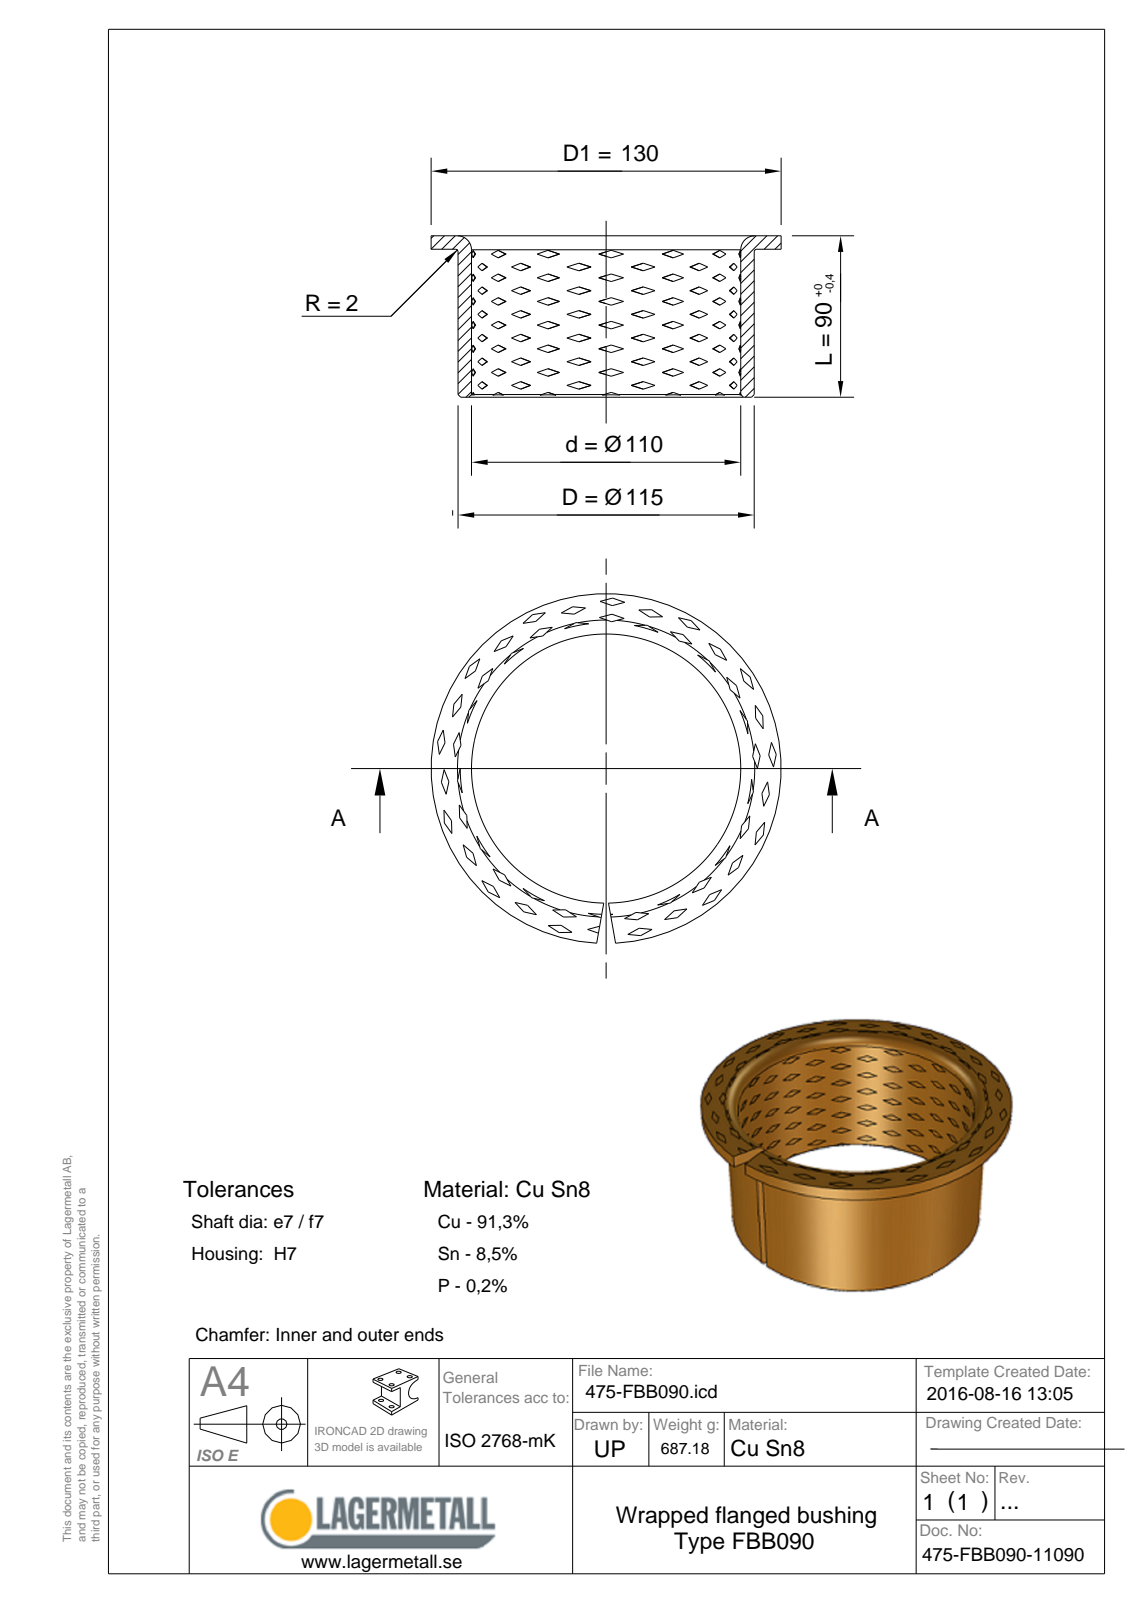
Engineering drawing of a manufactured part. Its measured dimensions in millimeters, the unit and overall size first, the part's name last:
Units: millimetres
Overall size (bounding box): 130 × 129.96 × 90
Round holes (diameter × count): ⌀110 ×1
Round bosses / shafts (diameter × count): ⌀130 ×1, ⌀115 ×1
Main face-to-face distances: 2.5, 87.5, 90
Volume: 84 837 mm³ · Surface area: 70 140 mm²
Bodies: 1 solid, 12 faces (5 planar, 3 cylindrical, 4 other)
Part name (STEP PRODUCT): 475-FBB090-11090
STEP written by: Spatial InterOp 3D (CONFIG_CONTROL_DESIGN)
